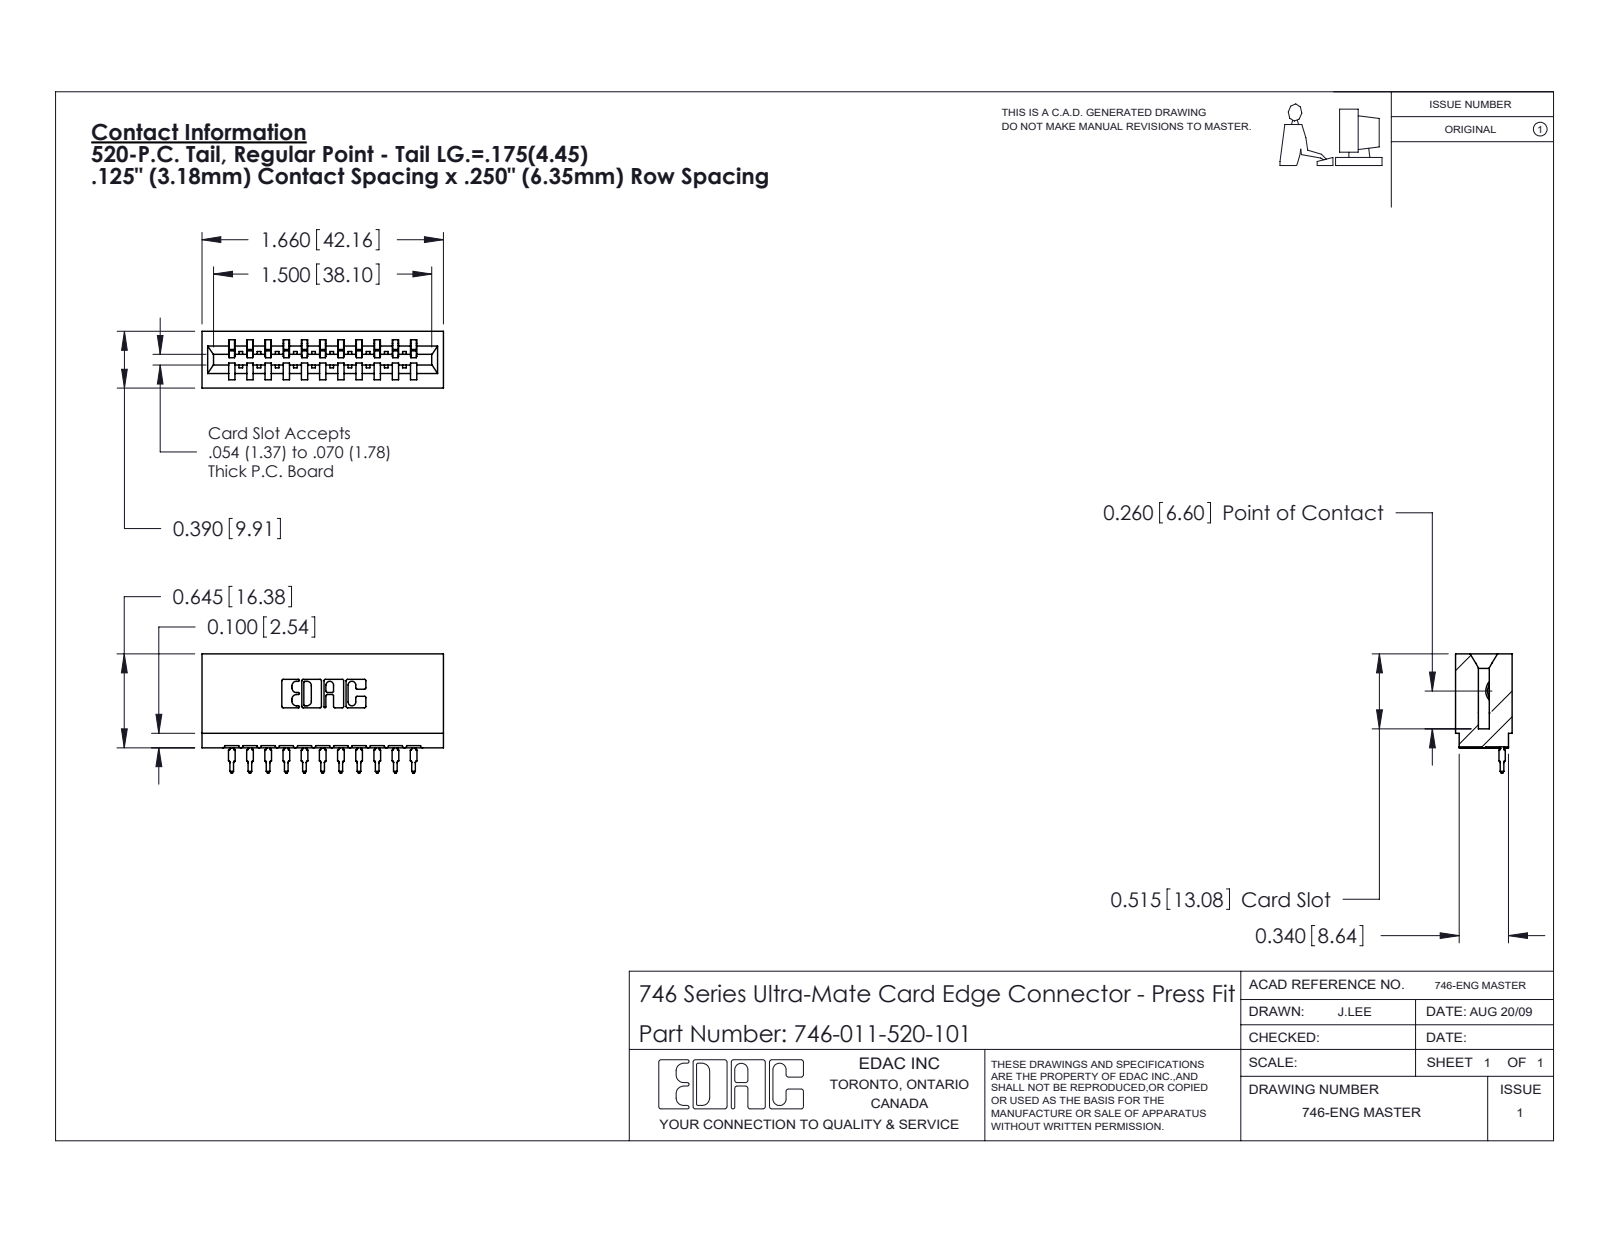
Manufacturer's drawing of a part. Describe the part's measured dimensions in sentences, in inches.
The part is named "746-292-001_520; 746-011-520-101; 746 Part_.515 Slot Depth - 01". Its 3-D file was written by "SolidWorks 2020 (CONFIG_CONTROL_DESIGN)". It is 12 solids with 1285 faces: 748 planar, 251 cylindrical and 286 other. Overall it measures 1.66 by 0.819 by 0.39 inches. Its volume is 0.281 cubic inches and its surface area 9.642 square inches. Partial cylindrical surfaces (rounded edges, fillets, slot ends): 22 of radius 0.01, 22 of radius 0.021, 12 of radius 0.015, 6 of radius 0.007, 6 of radius 0.031, 4 of radius 0.005, 4 of radius 0.011, 3 of radius 0.026. The main face-to-face distances are 0.25, 0.333, 0.5, 0.057, 0.125, 0.125, 0.39, 0.042, 0.208, 0.292.
